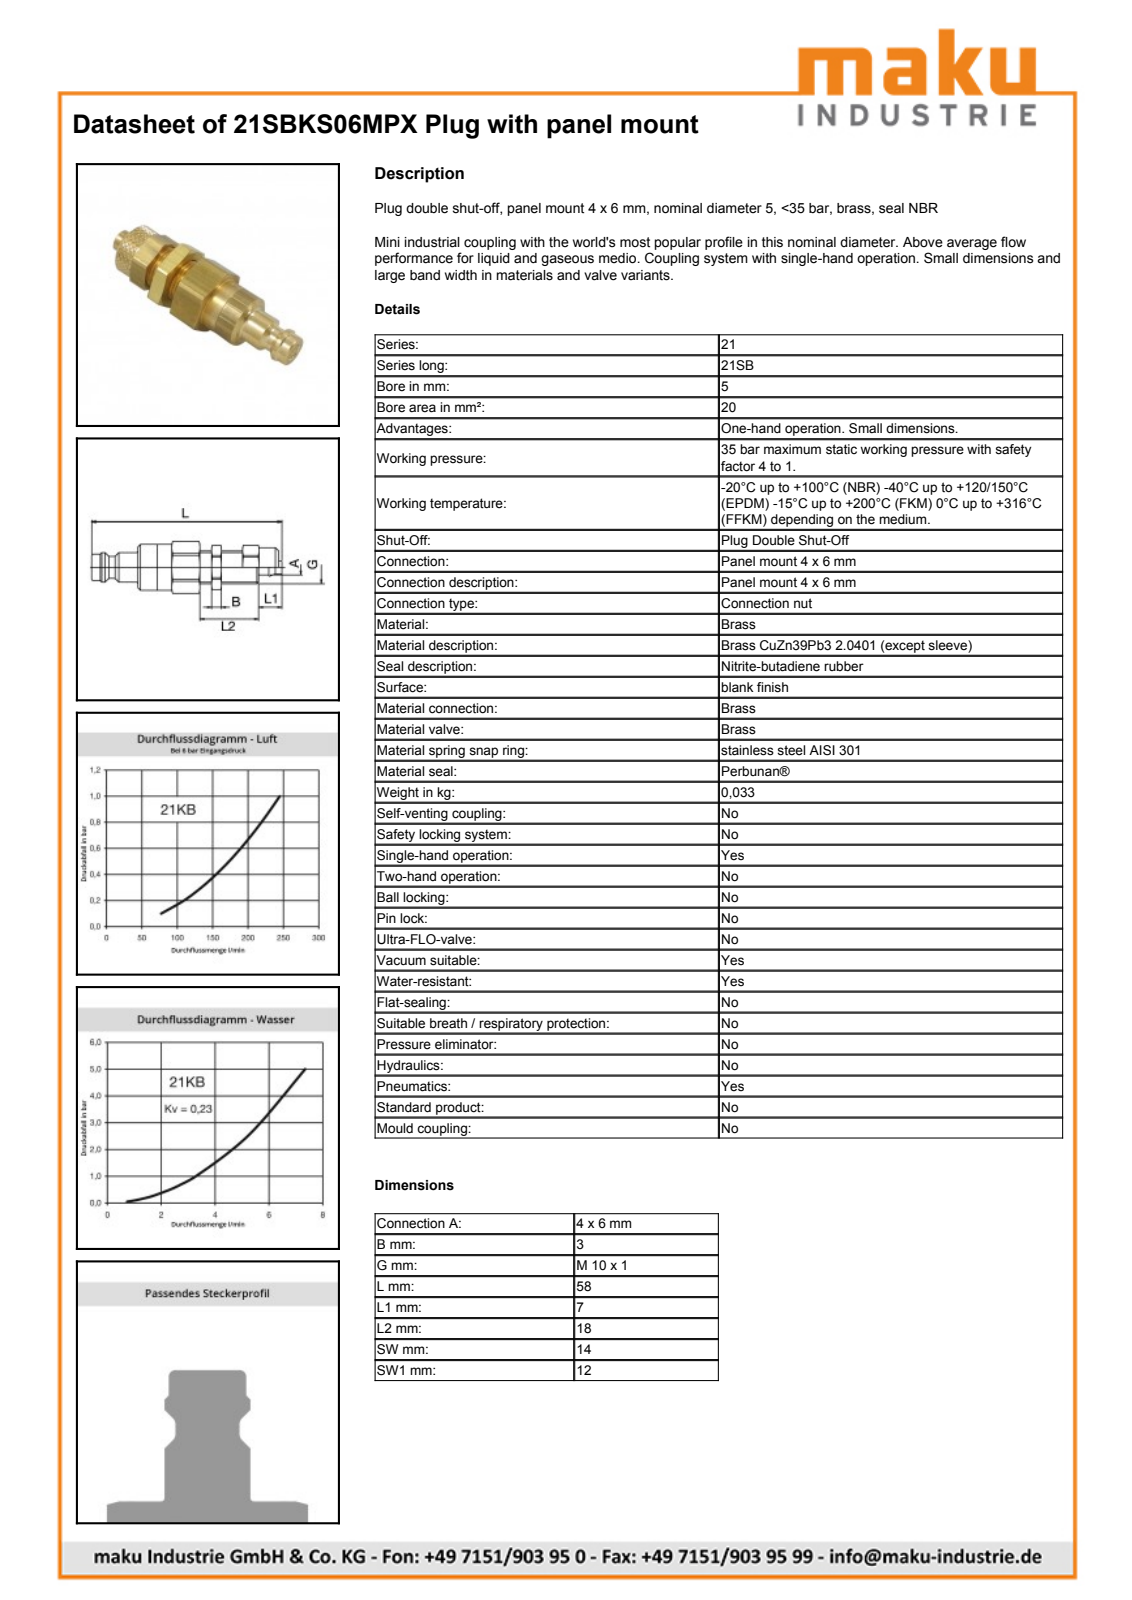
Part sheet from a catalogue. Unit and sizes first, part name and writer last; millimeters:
Units: millimetres
Overall size (bounding box): 58 × 15.76 × 14.74
Round holes (diameter × count): ⌀6.2 ×1, ⌀9.5 ×1, ⌀10.45 ×1, ⌀10.5 ×1, ⌀12 ×1
Round bosses / shafts (diameter × count): ⌀14 ×1, ⌀10.85 ×1, ⌀10 ×1, ⌀9 ×1, ⌀8.1 ×1, ⌀6.7 ×1, ⌀4.6 ×1, ⌀3.95 ×1
Partial cylindrical surfaces — rounded edges, fillets, slot ends (radius × count): R6.7 ×1, R6.75 ×1, R7.9 ×1
Main face-to-face distances: 14, 12, 24.93, 11, 33, 17.9, 22.93, 5.03, 18.9, 36.8
Volume: 5 459 mm³ · Surface area: 4 031 mm²
Bodies: 1 solid, 129 faces (32 planar, 36 cylindrical, 61 other)
Part name (STEP PRODUCT): D109330
STEP written by: Autodesk Inventor 2013 (AUTOMOTIVE_DESIGN)
